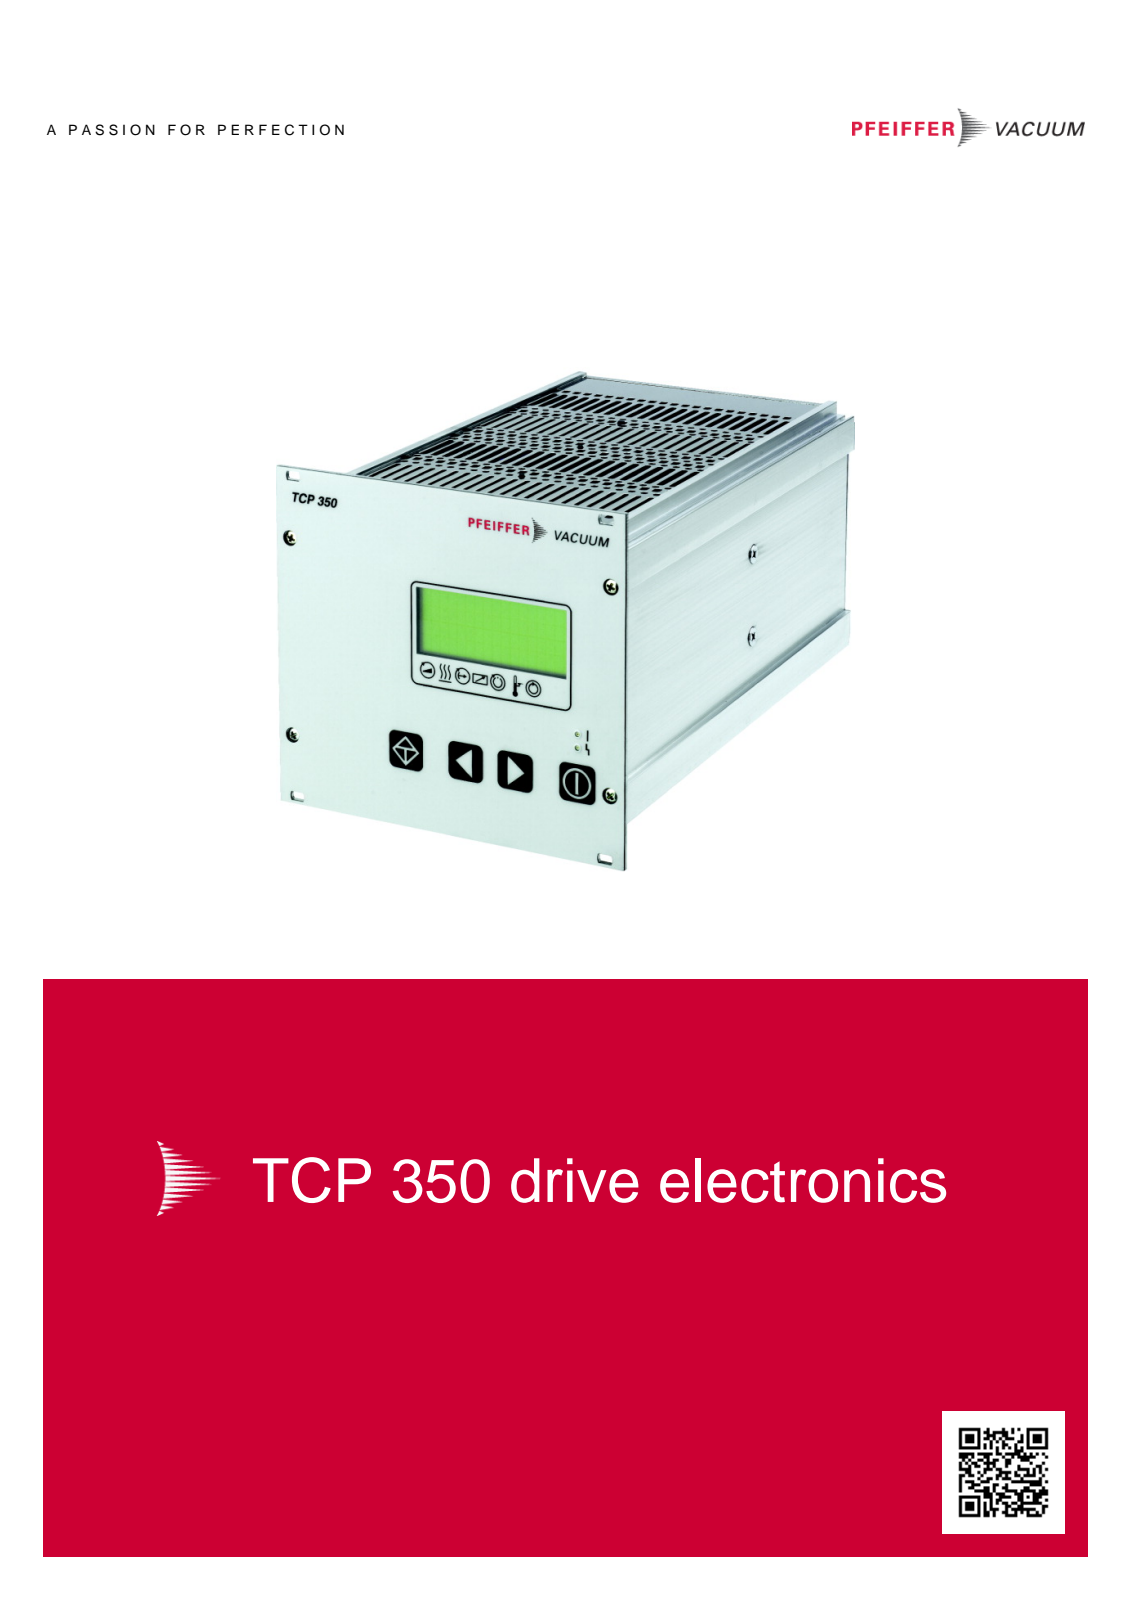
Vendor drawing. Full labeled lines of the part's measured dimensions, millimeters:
Part name (STEP PRODUCT): PM902290
STEP written by: Autodesk Inventor 2009 (AUTOMOTIVE_DESIGN)
Units: millimetres
Bodies: 1 solid, 1058 faces (677 planar, 75 cylindrical, 306 other)
Overall size (bounding box): 242.9 × 142 × 128.7
Volume: 3 485 000 mm³ · Surface area: 158 534 mm²
Round holes (diameter × count): ⌀1.15 ×26, ⌀9.6 ×1, ⌀13.8 ×1, ⌀18.5 ×1
Round bosses / shafts (diameter × count): ⌀22.5 ×1, ⌀17 ×1, ⌀16.5 ×1, ⌀11.5 ×1, ⌀11 ×1, ⌀4 ×1
Partial cylindrical surfaces — rounded edges, fillets, slot ends (radius × count): R1.5 ×16, R1.46 ×4, R1.7 ×4, R2 ×4, R2.2 ×4, R3 ×4
Main face-to-face distances: 110, 136, 232.4, 2.4, 230, 2, 232.7, 232, 2.39, 232.39
Hole centre spacings: 2.3, 4.06, 4.58, 6.14, 2.31, 2.32, 2.33, 4.61
